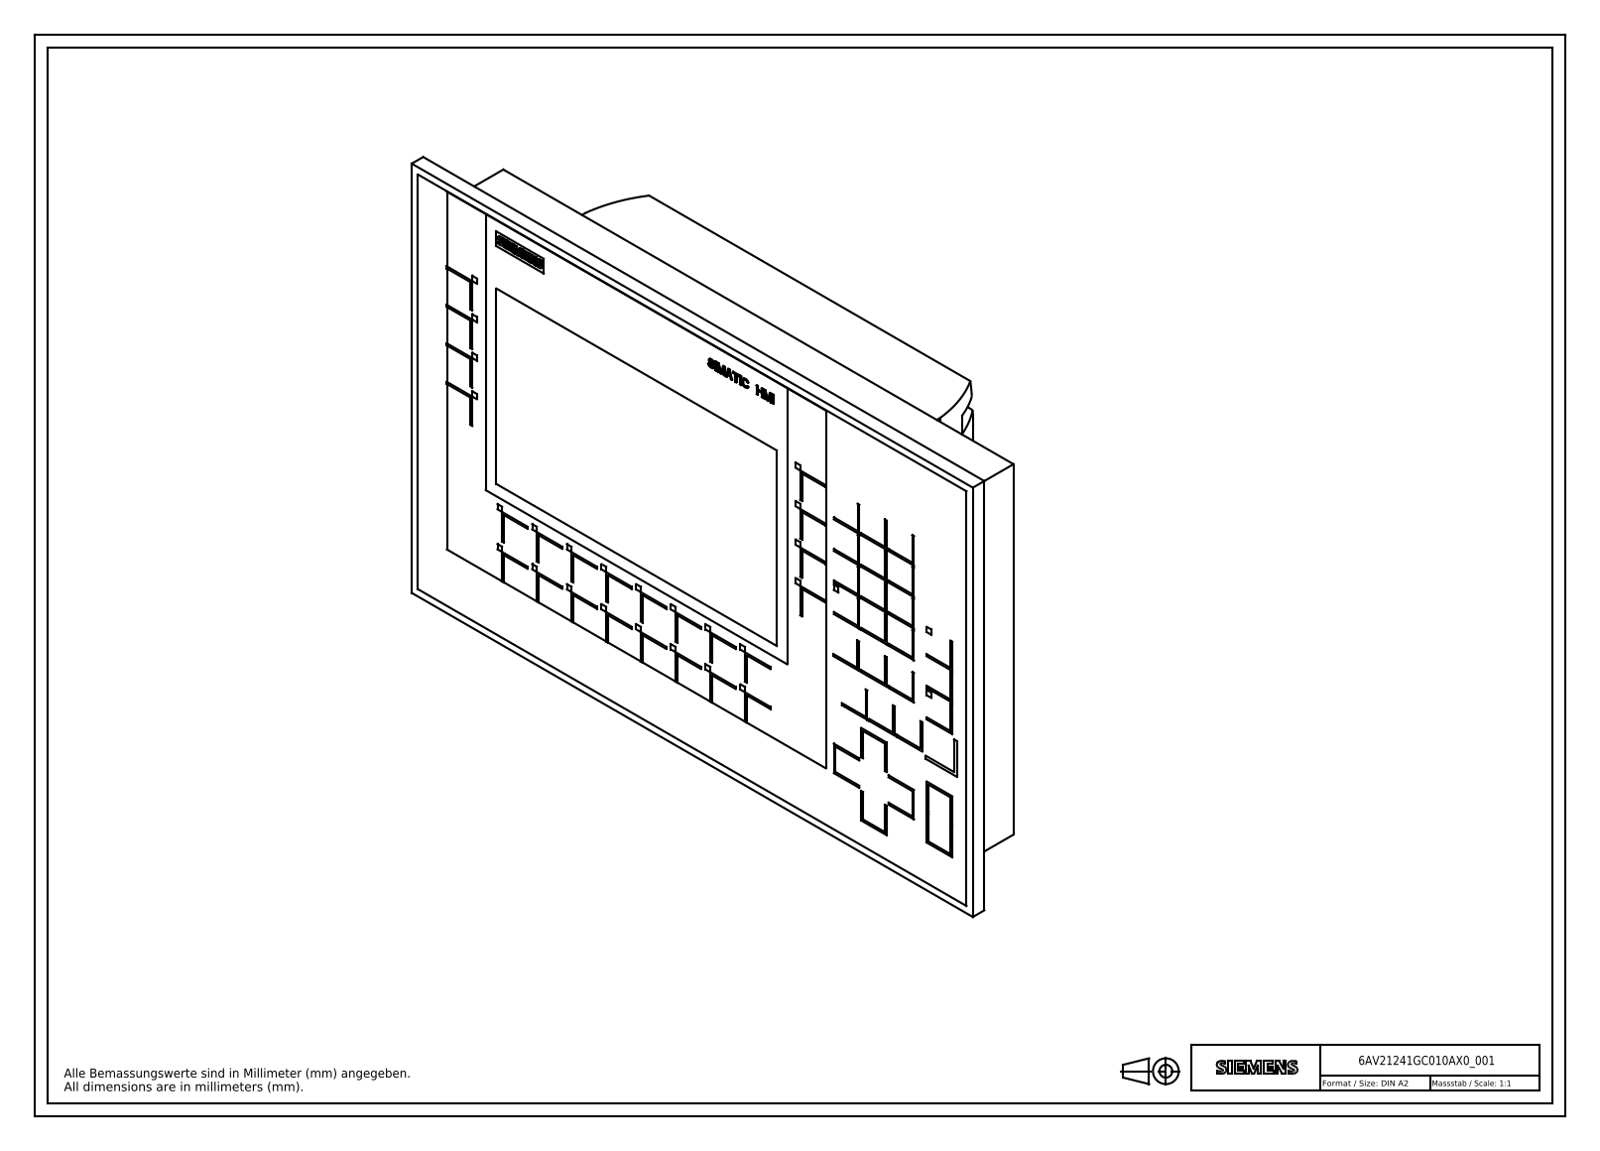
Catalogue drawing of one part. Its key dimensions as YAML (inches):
part_name: "A5E30321192A_001; A5E30291993A_001; A5E30287953A_001; A5E30287951A_001 (+1 more)"
step_written_by: "SIEMENS UGS NX 6.0 (AUTOMOTIVE_DESIGN)"
units: inches
bodies: {solids: 338, faces: 3419, planar: 2908, cylindrical: 170, other: 341}
overall_size: [12.126, 8.031, 2.732]
volume: 143.6
surface_area: 530.8
round_holes:
  - {diameter: 0.035, count: 9}
  - {diameter: 0.094, count: 2}
  - {diameter: 0.15, count: 2}
  - {diameter: 0.335, count: 2}
round_bosses_or_shafts:
  - {diameter: 0.276, count: 6}
  - {diameter: 0.217, count: 6}
  - {diameter: 0.118, count: 2}
  - {diameter: 0.038, count: 2}
  - {diameter: 0.031, count: 2}
  - {diameter: 0.315, count: 1}
partial_cylinders:
  - {radius: 0.008, count: 41}
  - {radius: 0.004, count: 30}
  - {radius: 0.031, count: 16}
  - {radius: 0.033, count: 6}
  - {radius: 0.018, count: 4}
  - {radius: 0.073, count: 4}
  - {radius: 0.08, count: 4}
  - {radius: 0.148, count: 4}
face_to_face_distances: [0.236, 2.48, 2.717, 0.313, 2.715, 0.234, 0.206, 2.686, 0.029, 0.031]
hole_center_spacings: [0.121, 0.109, 0.195, 0.217, 0.292, 0.326, 0.281, 0.332]
